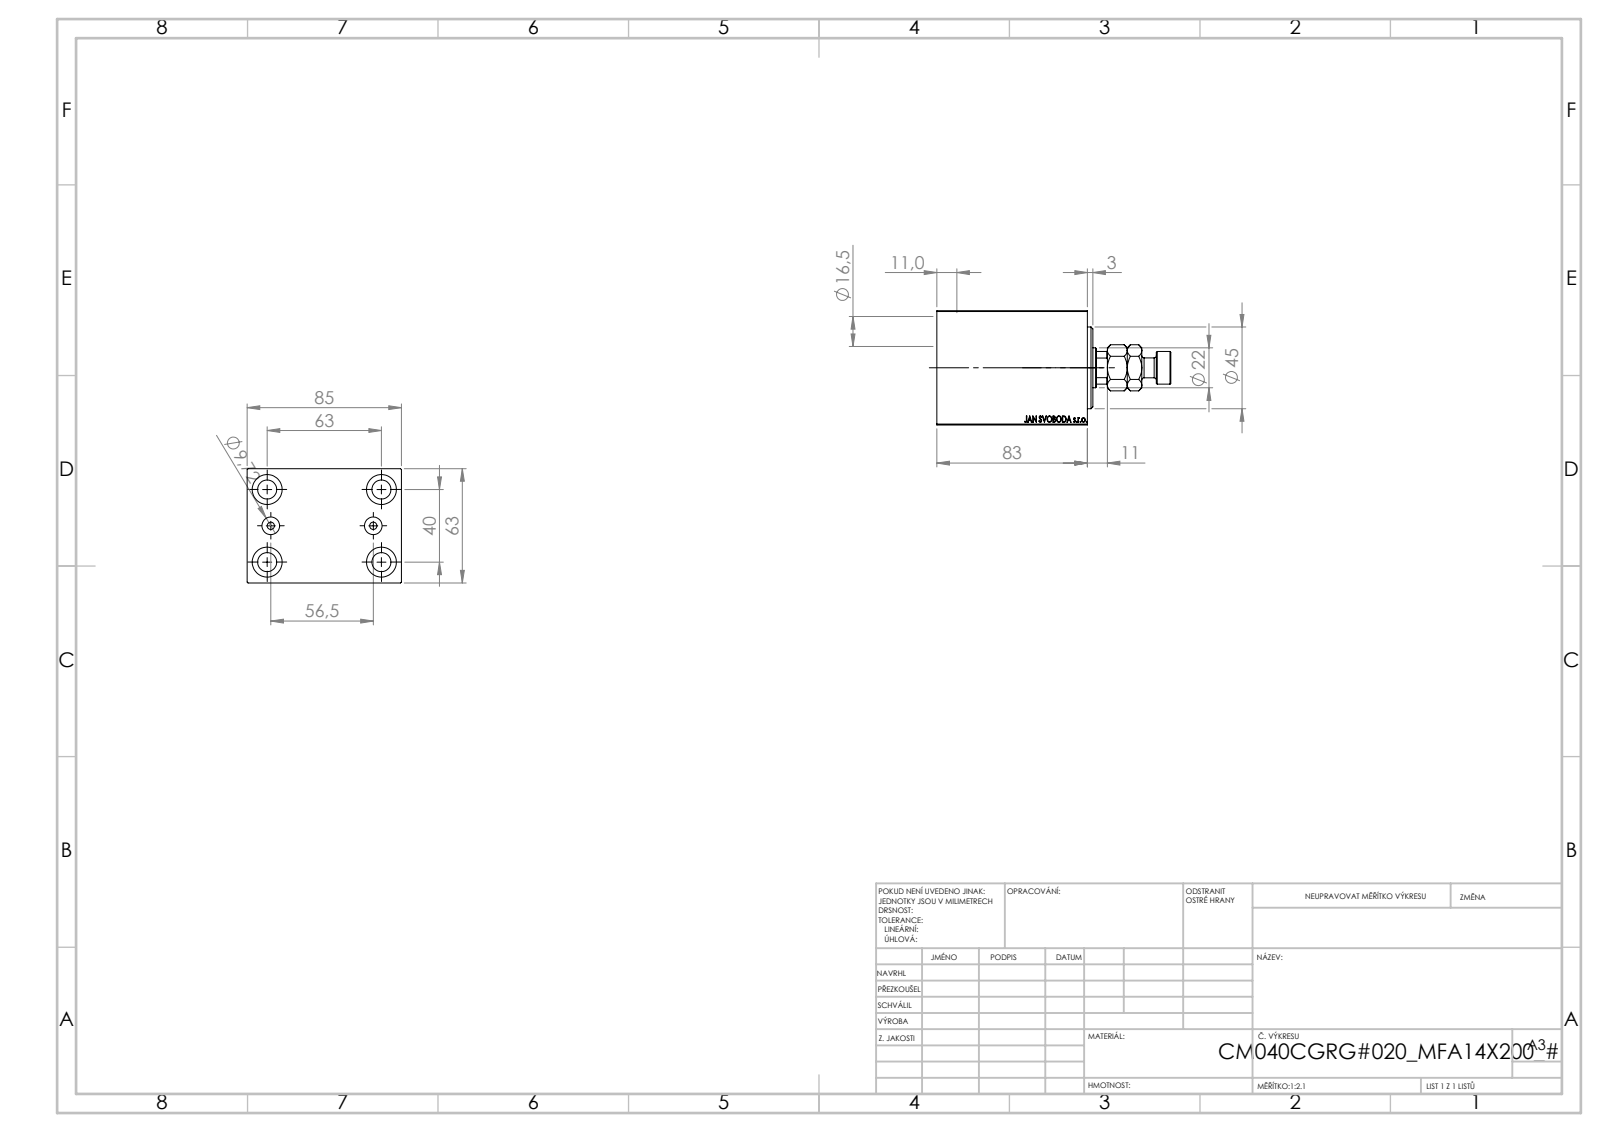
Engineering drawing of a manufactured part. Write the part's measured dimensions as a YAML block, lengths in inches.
part_name: "V450CM_C_Body; MFA; V450CM_C_VCP; V450CM_VC_B"
step_written_by: "SolidWorks 2019 (CONFIG_CONTROL_DESIGN)"
units: inches
bodies: {solids: 4, faces: 910, planar: 424, cylindrical: 60, other: 426}
overall_size: [5.079, 3.346, 2.48]
volume: 24.88
surface_area: 116.7
round_holes:
  - {diameter: 0.413, count: 4}
  - {diameter: 0.65, count: 4}
  - {diameter: 0.157, count: 2}
  - {diameter: 0.383, count: 2}
  - {diameter: 0.492, count: 1}
  - {diameter: 0.866, count: 1}
  - {diameter: 1.004, count: 1}
  - {diameter: 1.575, count: 1}
  - {diameter: 1.654, count: 1}
  - {diameter: 1.772, count: 1}
round_bosses_or_shafts:
  - {diameter: 0.709, count: 1}
  - {diameter: 0.433, count: 1}
partial_cylinders:
  - {radius: 0.413, count: 1}
face_to_face_distances: [2.48, 3.346, 3.268, 2.008, 1.26, 0.433, 0.866, 0.315, 0.85, 1.157]
hole_center_spacings: [1.469, 0.791, 0.807, 1.575, 2.434, 2.48, 2.528, 2.938]
